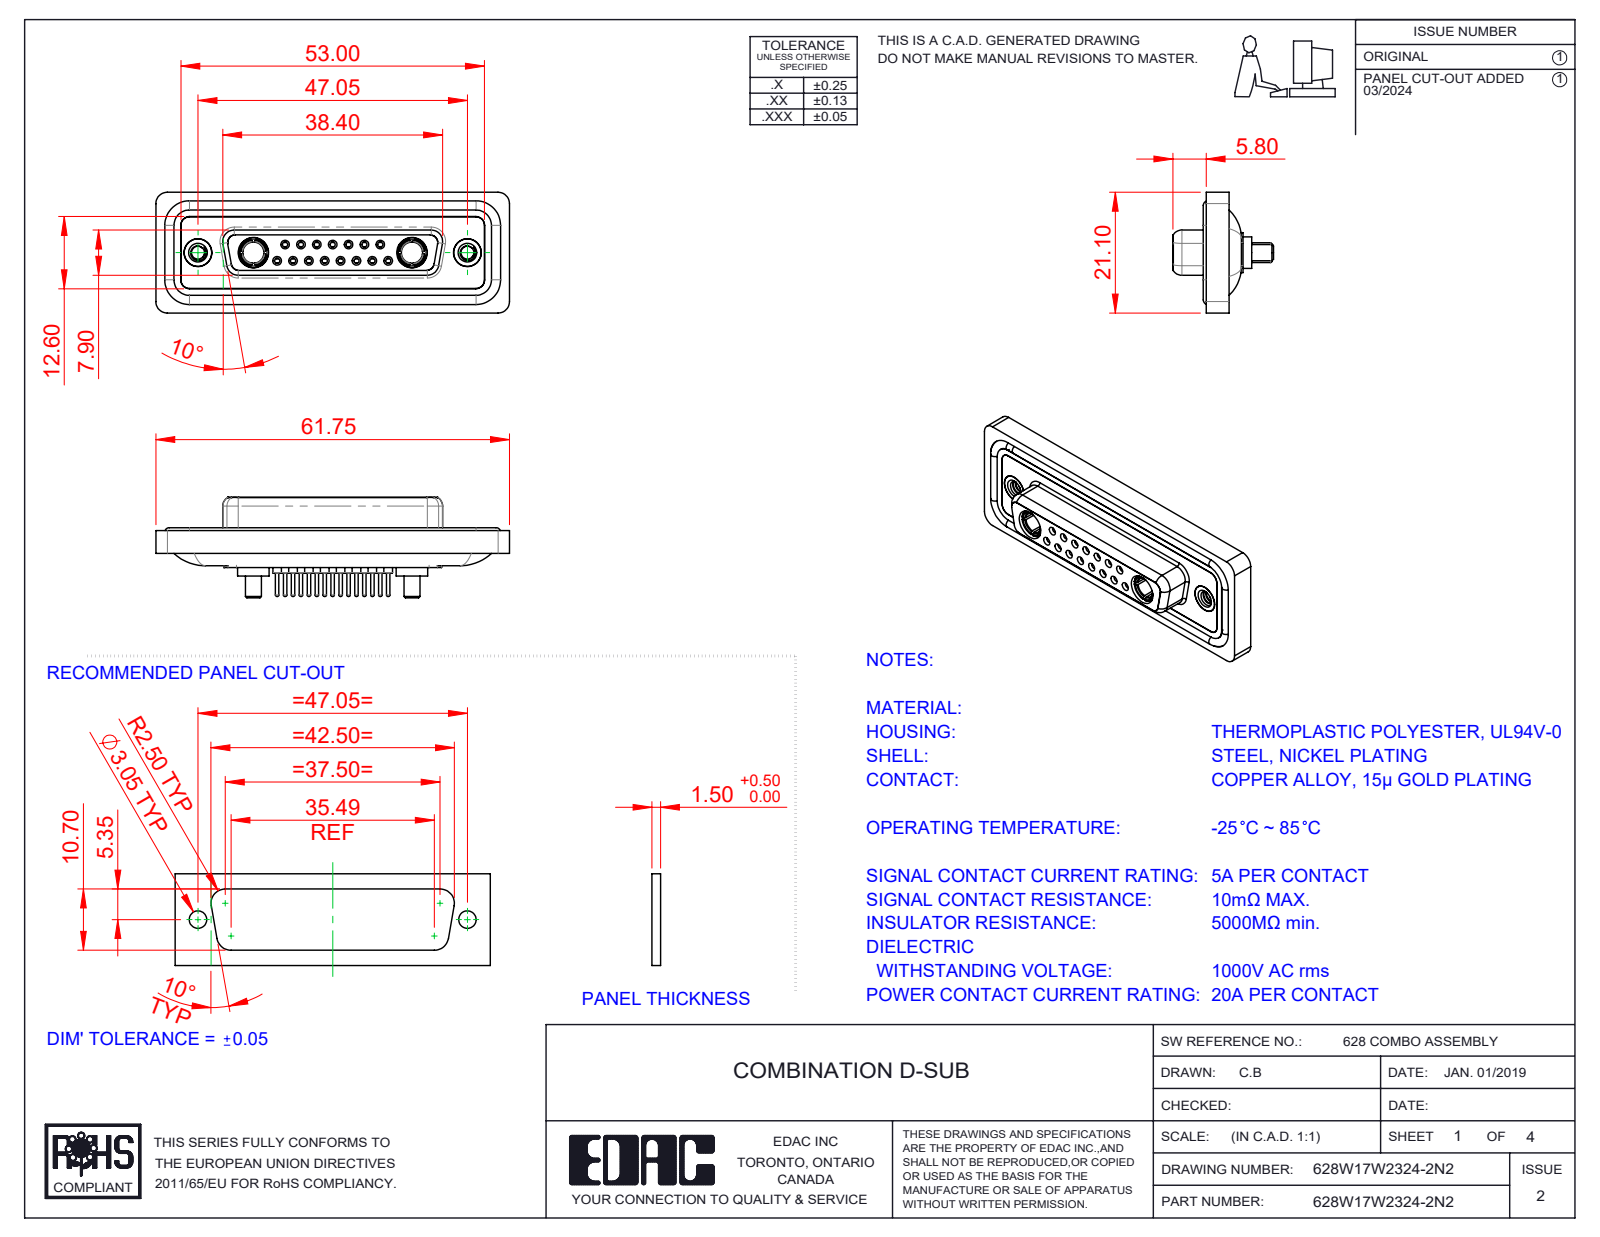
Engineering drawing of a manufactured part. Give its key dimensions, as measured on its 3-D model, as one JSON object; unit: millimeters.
{"part_name": "Power Socket_20A S; 628Combo Shell Front_25 Contacts; 628Combo Contact Row 2_24; 628W17W2324-2N2 (+5 more)", "step_written_by": "SolidWorks 2023 (CONFIG_CONTROL_DESIGN)", "units": "millimeters", "bodies": {"solids": 26, "faces": 1359, "planar": 388, "cylindrical": 519, "other": 452}, "overall_size": [61.75, 21.1, 17.55], "volume_mm3": 8324, "surface_area_mm2": 13855, "round_holes": [[0.9, 15], [1.1, 15], [1.5, 15], [2, 15], [1.6, 8], [1.7, 7], [4.85, 4], [2.26, 2], [3.7, 2], [4, 2], [4.05, 2], [5, 2]], "round_bosses_or_shafts": [[2.2, 15], [0.6, 15], [1.6, 11], [5.5, 2], [5.2, 2], [4.96, 2], [4.95, 2], [4.8, 2]], "partial_cylinders_radius": [[1.5, 22], [2, 18], [1.35, 8], [1.6, 8], [0.25, 4], [0.5, 4], [0.6, 4], [0.65, 4]], "face_to_face_distances": [0.4, 1.8, 7.45, 5.65, 6.6, 0.5, 7.05, 1.6, 2.9, 1.1], "hole_center_spacings": [3.16, 2.77, 8.31, 5.54, 5.03, 5.04, 7.49, 11.08]}
